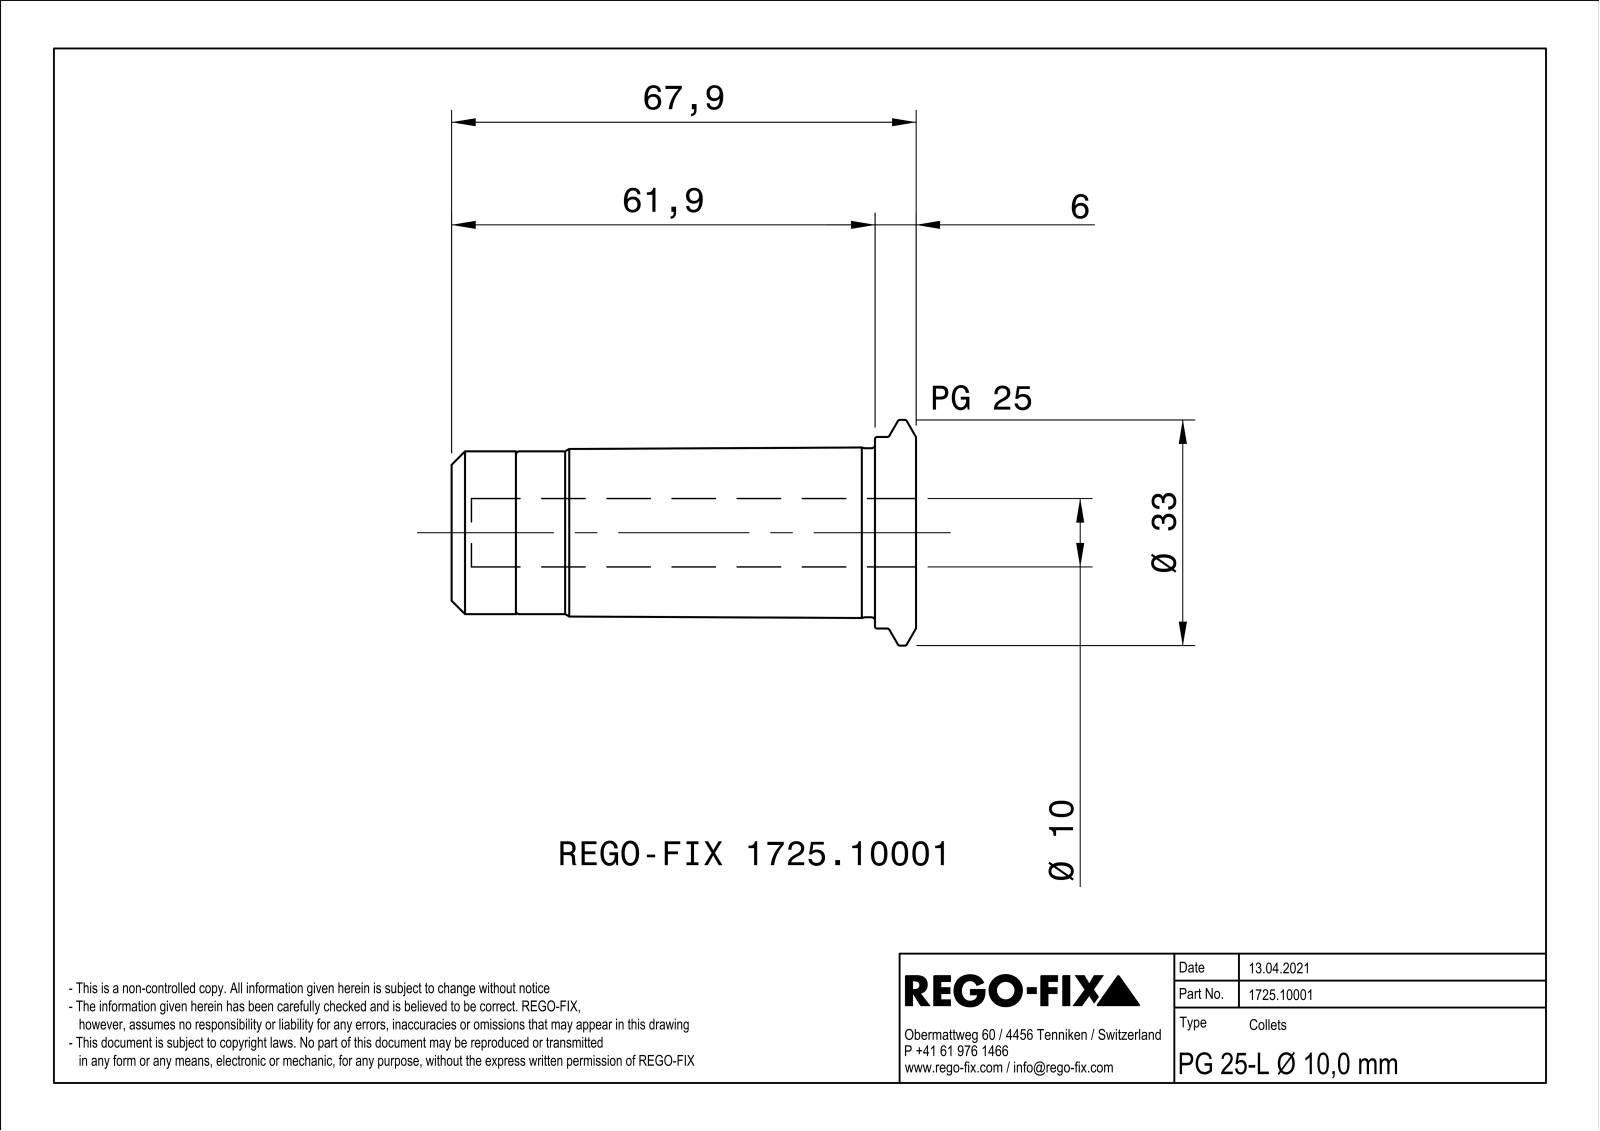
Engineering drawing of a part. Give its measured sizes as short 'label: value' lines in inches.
name: NOCUT
written by: SIEMENS PLM Software Solid Edge ST10 (AUTOMOTIVE_DESIGN)
unit: in
bodies: 1 solid, 93 faces (29 planar, 21 cylindrical, 43 other)
size: 2.673 × 1.299 × 1.299
holes: 1× ⌀0.11, 1× ⌀0.394, 1× ⌀0.728, 1× ⌀0.803, 1× ⌀0.874
bosses: 1× ⌀1.299, 1× ⌀1.102, 1× ⌀0.972, 1× ⌀0.937, 1× ⌀0.866, 1× ⌀0.824
rounds: 3× R0.079
face distances: 0.039, 2.673, 2.008, 0.665, 0.236, 2.067, 1.772, 2.437, 2.303, 0.295
